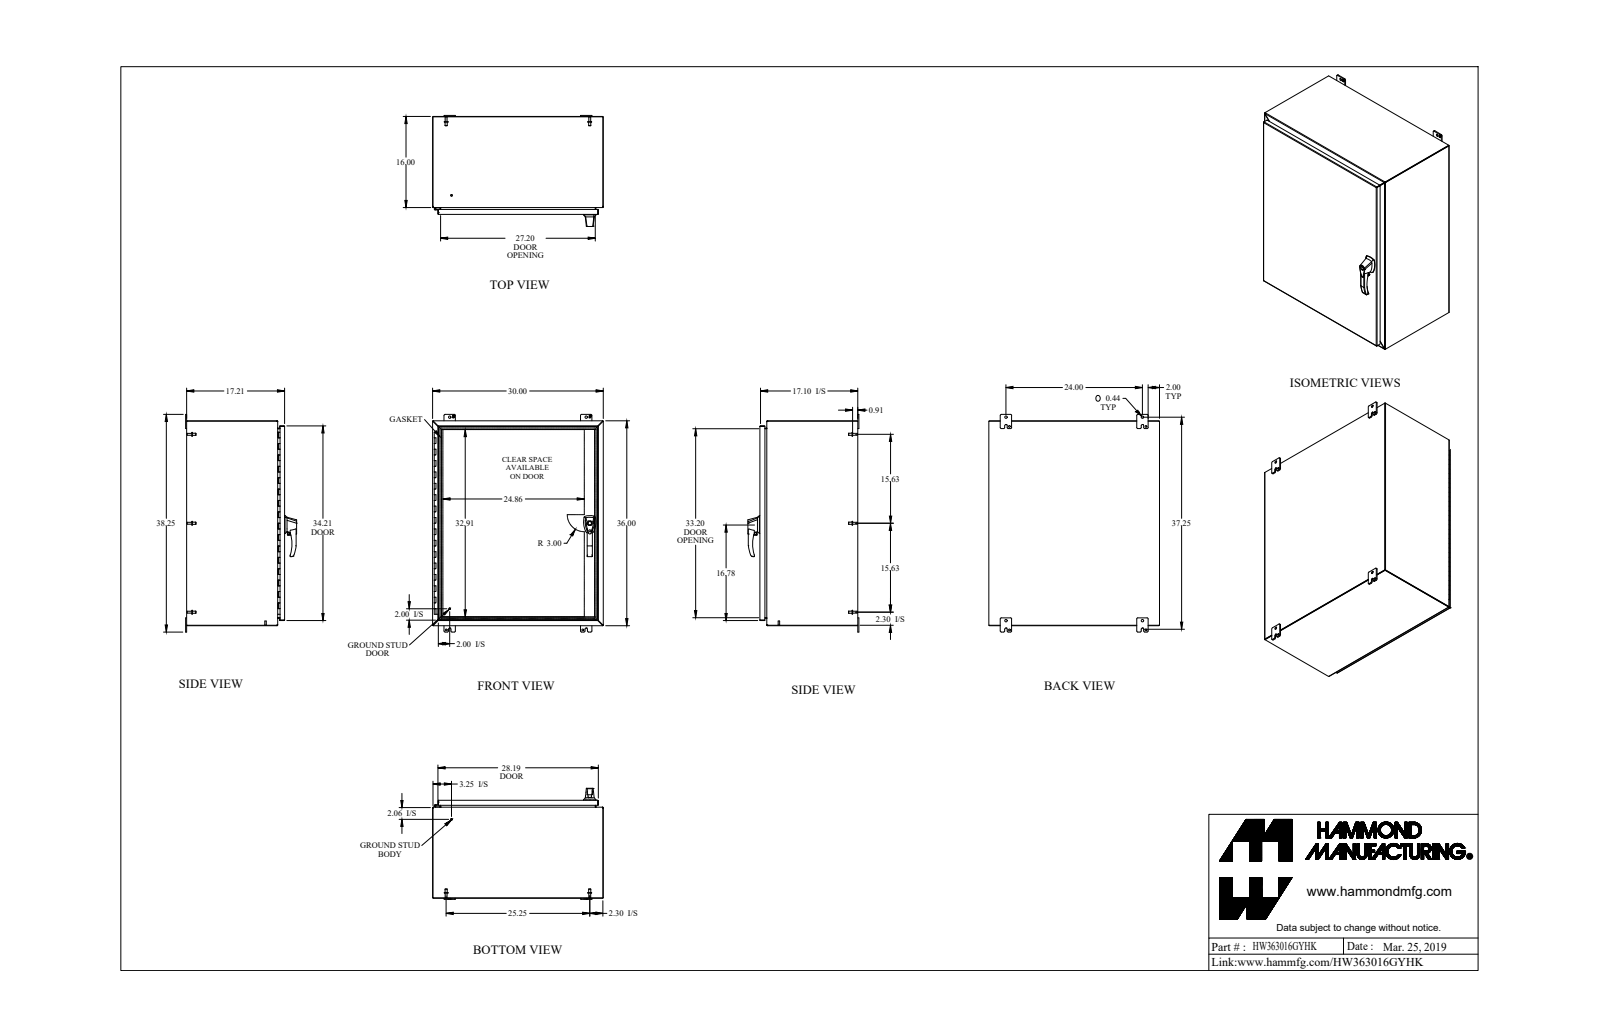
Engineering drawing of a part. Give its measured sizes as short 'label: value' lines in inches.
name: HW363016GYHK
written by: SolidWorks 2018 (AUTOMOTIVE_DESIGN)
unit: in
bodies: 52 solids, 1609 faces (773 planar, 655 cylindrical, 181 other)
size: 38.25 × 30 × 19.512
volume: 385.8 in³; area: 10 293 in²
holes: 6× ⌀0.176, 4× ⌀0.25, 4× ⌀0.313, 3× ⌀0.196, 3× ⌀0.265, 3× ⌀0.413, 2× ⌀0.256, 2× ⌀0.394, 2× ⌀0.437, 1× ⌀0.187, 1× ⌀0.233, 1× ⌀0.334
bosses: 11× ⌀0.375, 6× ⌀0.65, 6× ⌀0.33, 6× ⌀0.25, 6× ⌀0.156, 3× ⌀1, 2× ⌀0.63, 2× ⌀0.51
rounds: 34× R0.188, 31× R0.25, 18× R0.036, 18× R0.108, 12× R0.06, 12× R0.116, 9× R0.125, 8× R0.04
face distances: 0.072, 29.928, 0.072, 17.138, 17.066, 17.21, 17.138, 35.928, 29.856, 30
hole spacings: 14.118, 14.119, 28.237, 1.111, 7.852, 14.119, 24, 24.721
